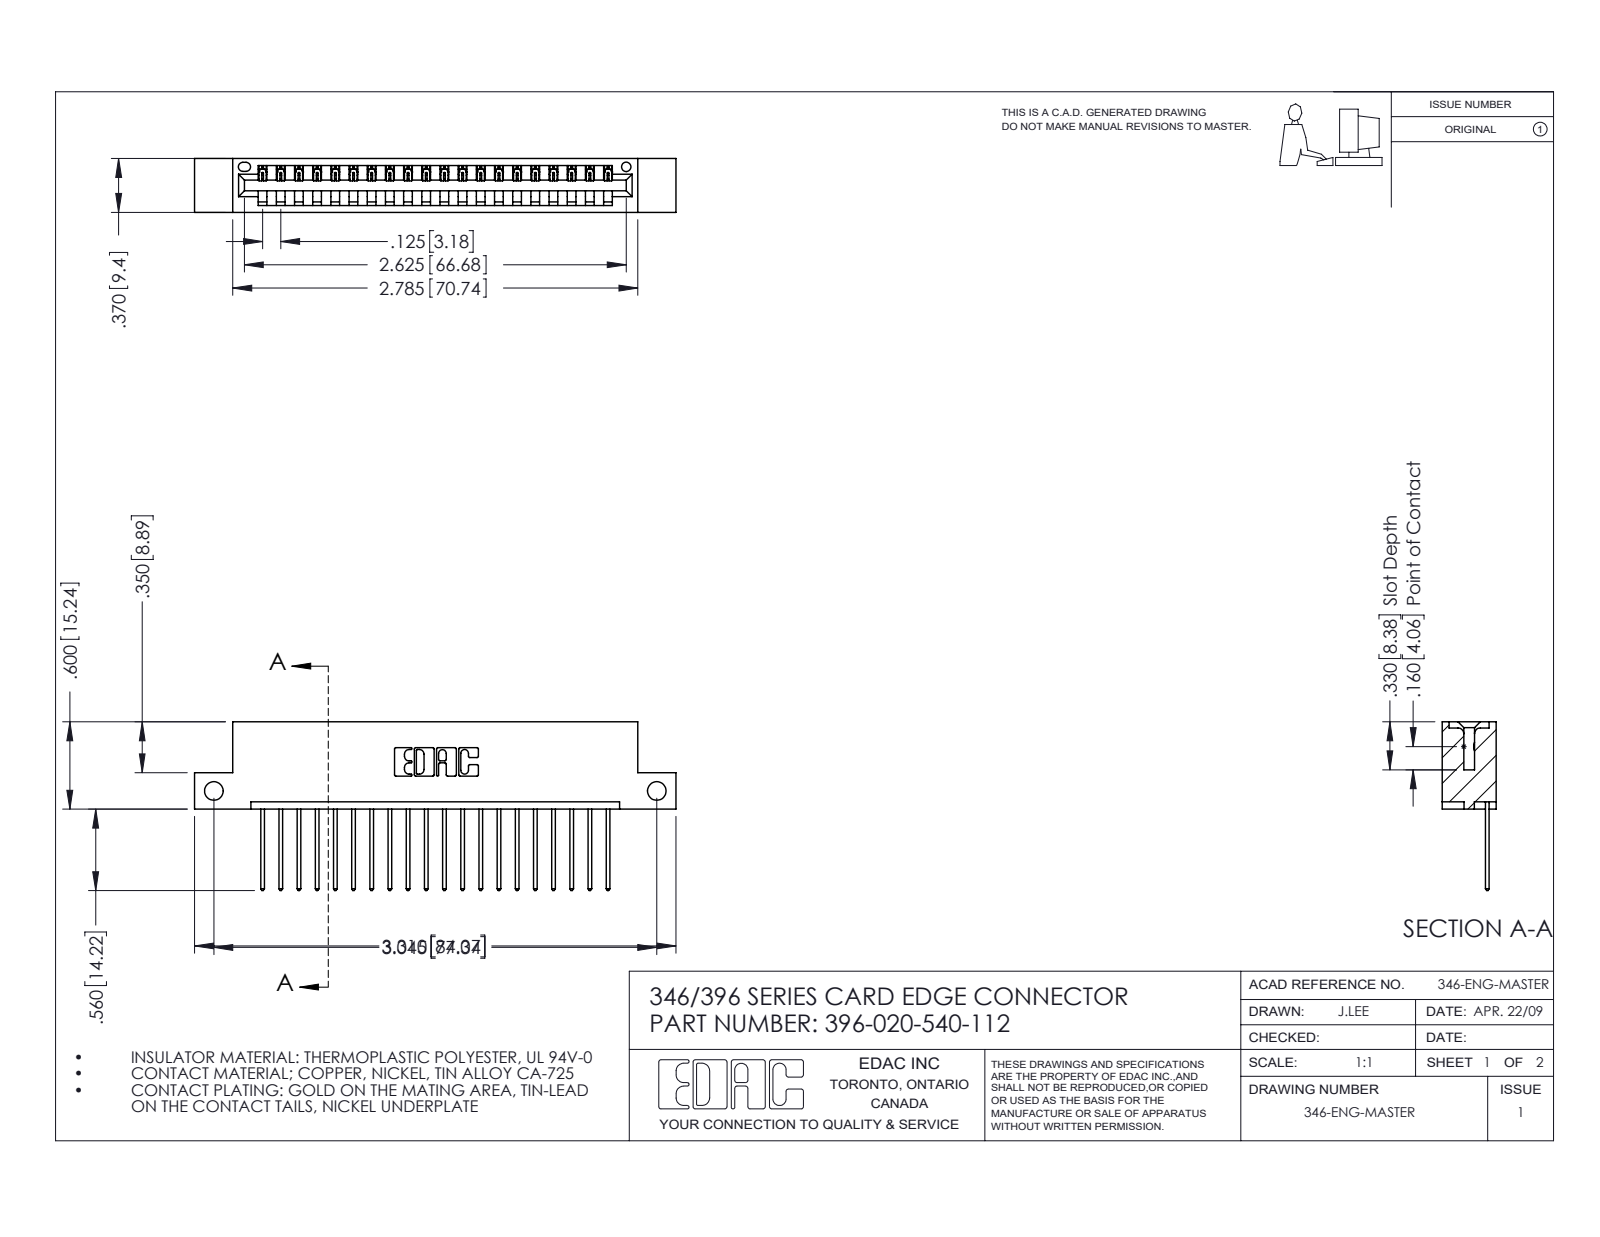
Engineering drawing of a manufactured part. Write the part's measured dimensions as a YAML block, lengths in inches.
part_name: "346 Part_Flush Mounting Lugs - Side Mount; 396-020-540-112; 345-292-001_345-293-140"
step_written_by: "SolidWorks 2016 (CONFIG_CONTROL_DESIGN)"
units: inches
bodies: {solids: 21, faces: 1282, planar: 876, cylindrical: 406, other: 0}
overall_size: [3.31, 1.16, 0.37]
volume: 0.478
surface_area: 14.89
round_holes:
  - {diameter: 0.128, count: 2}
  - {diameter: 0.064, count: 1}
partial_cylinders:
  - {radius: 0.006, count: 40}
  - {radius: 0.01, count: 40}
  - {radius: 0.01, count: 22}
  - {radius: 0.007, count: 6}
  - {radius: 0.031, count: 6}
  - {radius: 0.026, count: 3}
  - {radius: 0.031, count: 2}
  - {radius: 0.04, count: 2}
face_to_face_distances: [0.048, 0.322, 0.25, 0.37, 0.072, 0.298, 0.025, 0.148, 0.222, 0.1]
hole_center_spacings: [3.045]
